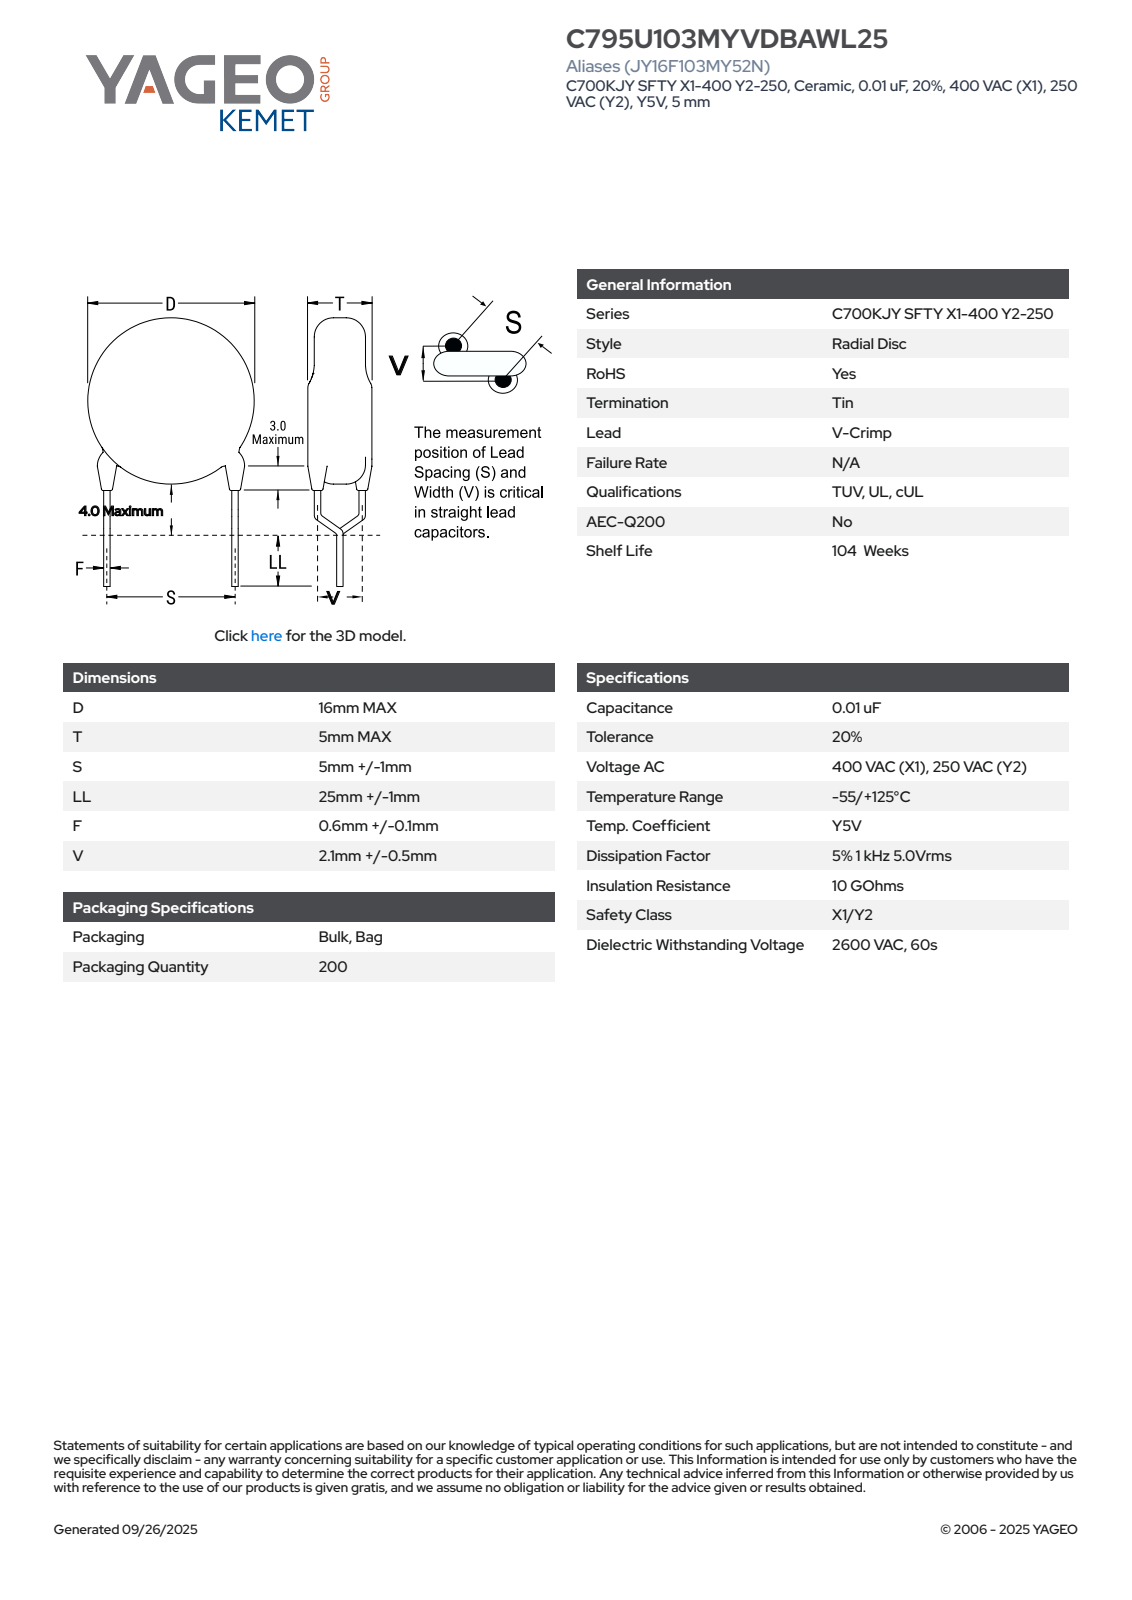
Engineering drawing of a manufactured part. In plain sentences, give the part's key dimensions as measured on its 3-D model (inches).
The part is named "CCD_VC16X5_D16T5S5LL26F0.7V2.1". Its 3-D file was written by "SolidWorks 2021 (AUTOMOTIVE_DESIGN)". It is 4 solids with 85 faces: 63 planar, 18 cylindrical and 4 other. Overall it measures 1.654 by 0.63 by 0.197 inches. Its volume is 0.061 cubic inches and its surface area 1.16 square inches. Round bosses or shafts: 6 of diameter 0.028, 2 of diameter 0.047, 1 of diameter 0.63. The main face-to-face distances are 0.197, 1.024, 1.388, 0.365, 1.312, 0.289, 0.076, 0.021, 0.014, 0.312.
